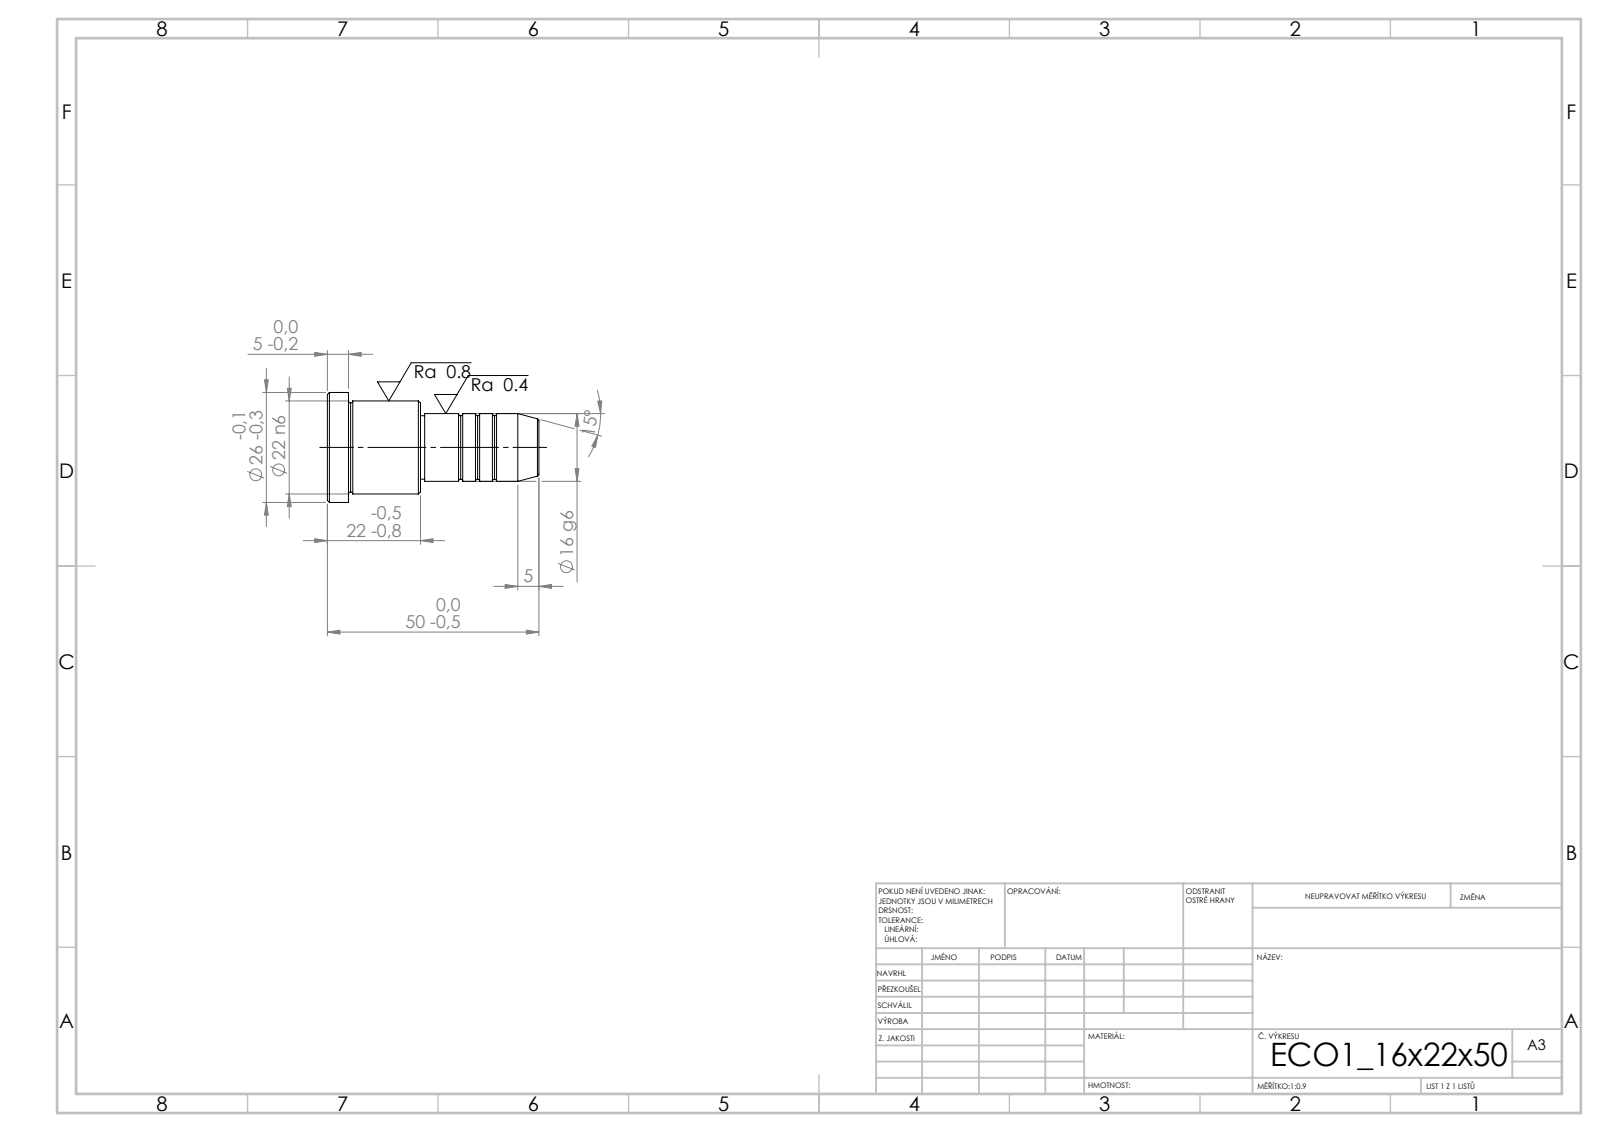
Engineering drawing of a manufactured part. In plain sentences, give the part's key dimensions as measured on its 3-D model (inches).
Its 3-D file was written by "SolidWorks 2019 (CONFIG_CONTROL_DESIGN)". It is 1 solid with 43 faces: 5 planar, 14 cylindrical and 24 other. Overall it measures 1.969 by 1.024 by 1.024 inches. Its volume is 0.882 cubic inches and its surface area 6.335 square inches. Round bosses or shafts: 1 of diameter 1.024, 1 of diameter 0.866, 1 of diameter 0.63, 1 of diameter 0.591. The main face-to-face distances are 0.866, 0.669, 0.197, 1.102, 1.772, 1.969, 1.063, 0.039, 0.709, 0.906.
